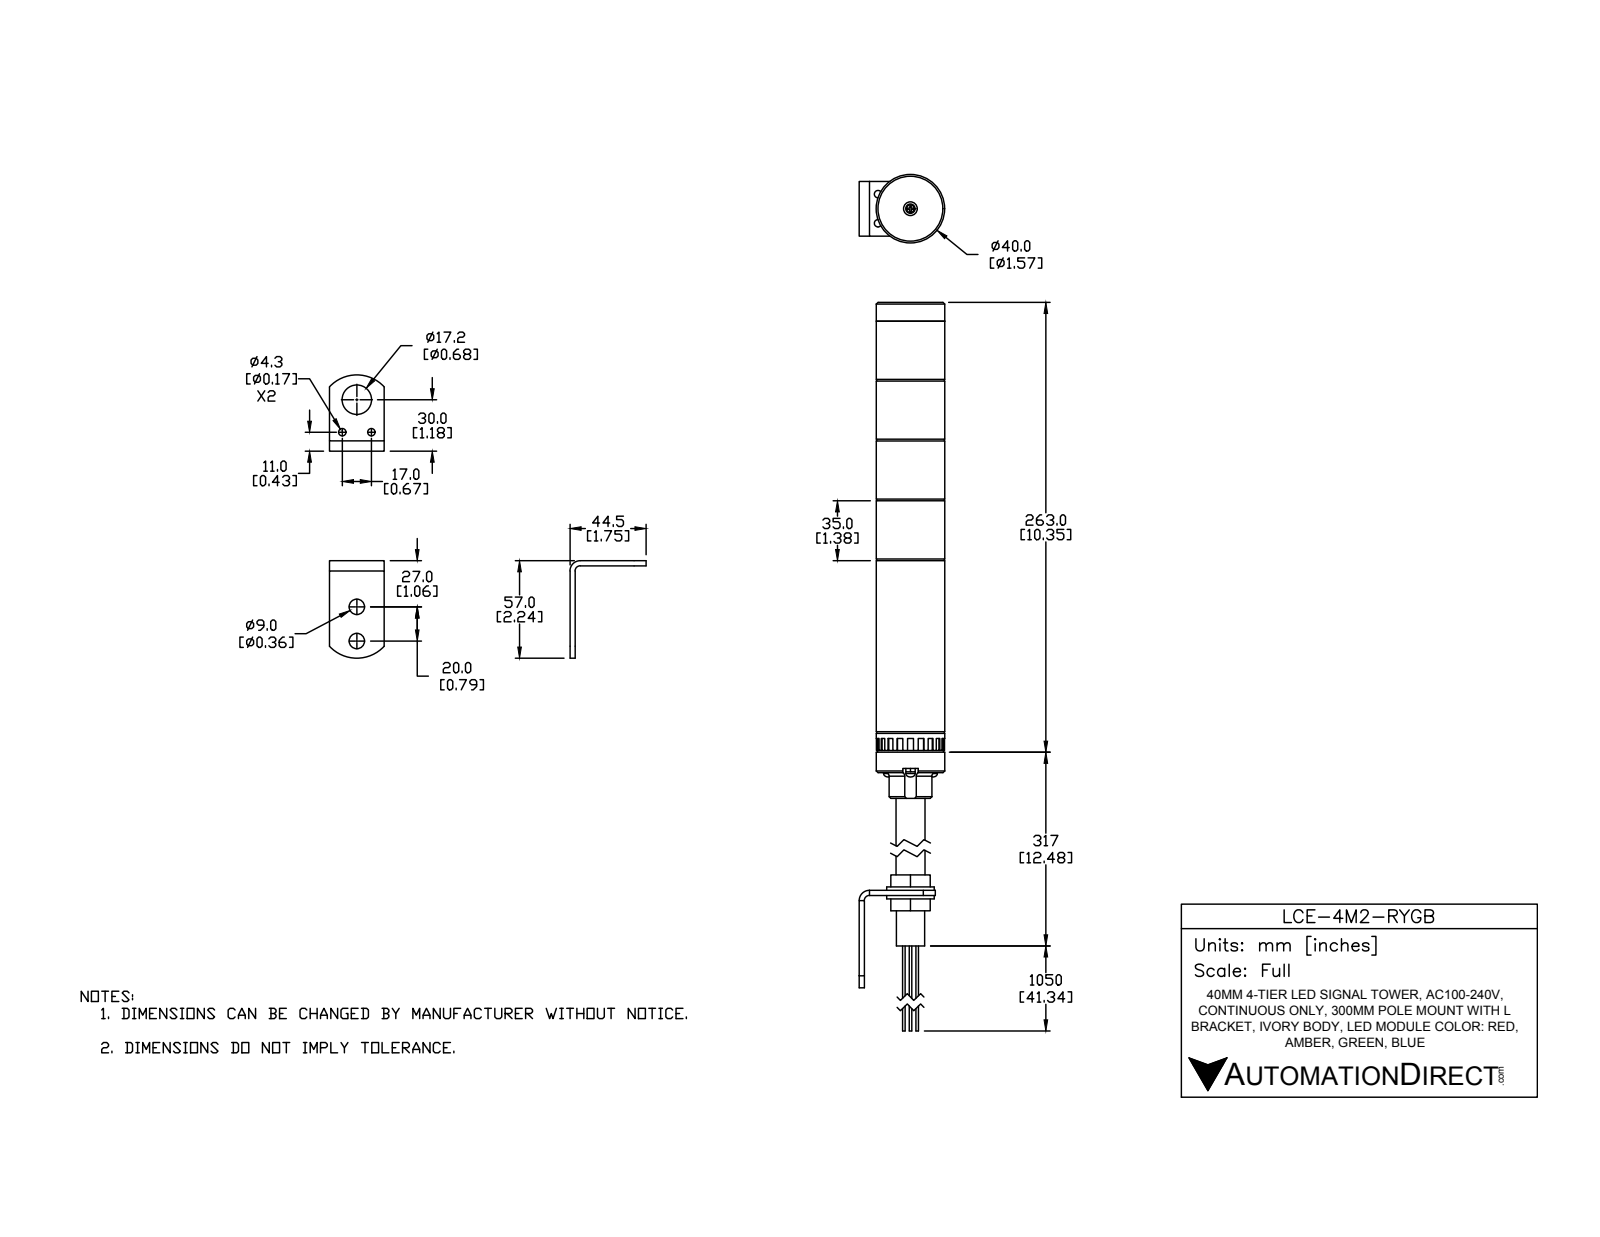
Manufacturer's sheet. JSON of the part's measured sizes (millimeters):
{"part_name": "LCE-4M2-RYGB", "step_written_by": "SolidWorks 2016 (AUTOMOTIVE_DESIGN)", "units": "millimeters", "bodies": {"solids": 33, "faces": 377, "planar": 241, "cylindrical": 116, "other": 20}, "overall_size": [663, 50, 40], "volume_mm3": 395408, "surface_area_mm2": 123957, "round_holes": [[3.5, 3], [4, 3], [4.3, 2], [9.04, 2], [8, 1], [12, 1], [17.2, 1], [17.5, 1], [18, 1]], "round_bosses_or_shafts": [[1.5, 6], [5.5, 4], [3, 3], [40, 1], [39.5, 1], [38.5, 1], [27.8, 1], [17, 1]], "partial_cylinders_radius": [[4.5, 3], [21.79, 2], [3, 1], [6, 1], [12.5, 1]], "face_to_face_distances": [35, 1, 70, 34, 36, 105, 69, 11, 71, 104], "hole_center_spacings": [15, 25.98, 20.81, 6.09, 17, 17.09, 20, 20.08]}
